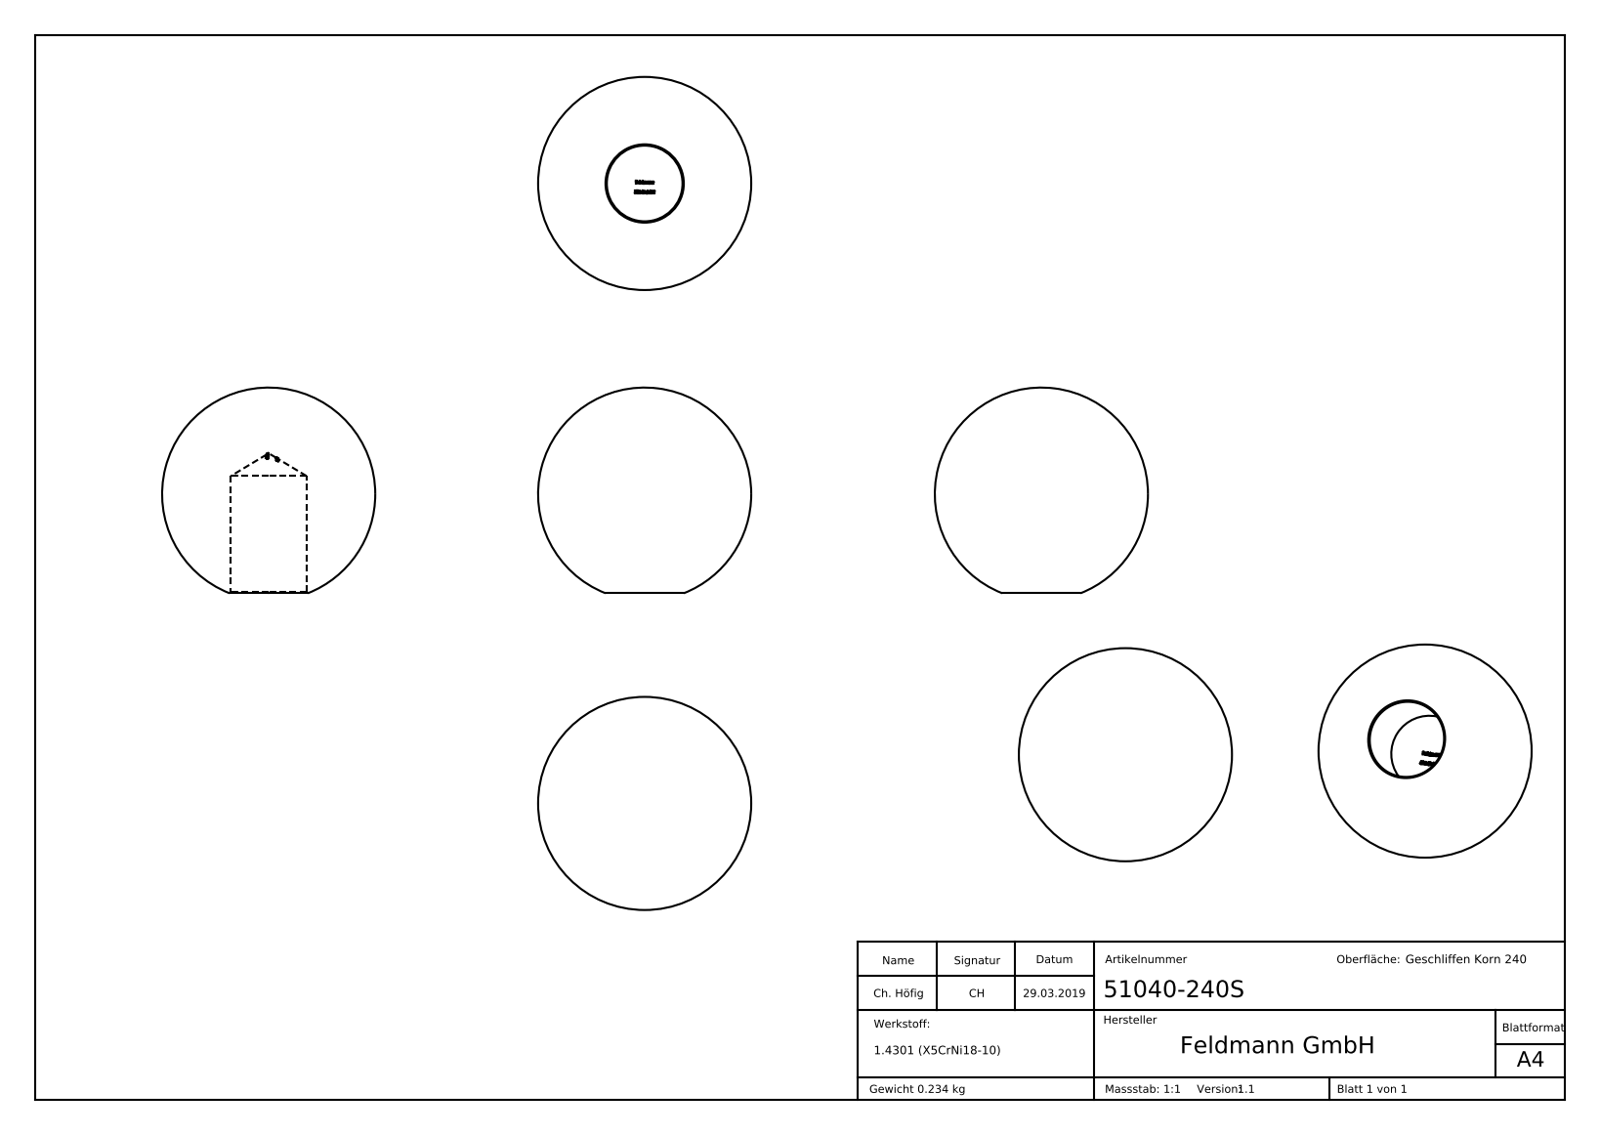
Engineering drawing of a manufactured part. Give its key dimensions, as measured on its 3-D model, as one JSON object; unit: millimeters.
{"part_name": "51040-240S", "step_written_by": "SolidWorks 2015 (CONFIG_CONTROL_DESIGN)", "units": "millimeters", "bodies": {"solids": 1, "faces": 249, "planar": 104, "cylindrical": 2, "other": 143}, "overall_size": [40, 40, 38.6], "volume_mm3": 29679, "surface_area_mm2": 6026, "round_holes": [[14.2, 1]], "face_to_face_distances": [1.93, 1.27, 1.88, 0.37, 0.47, 1.19, 1.46, 0.53, 2.73, 0.48]}
